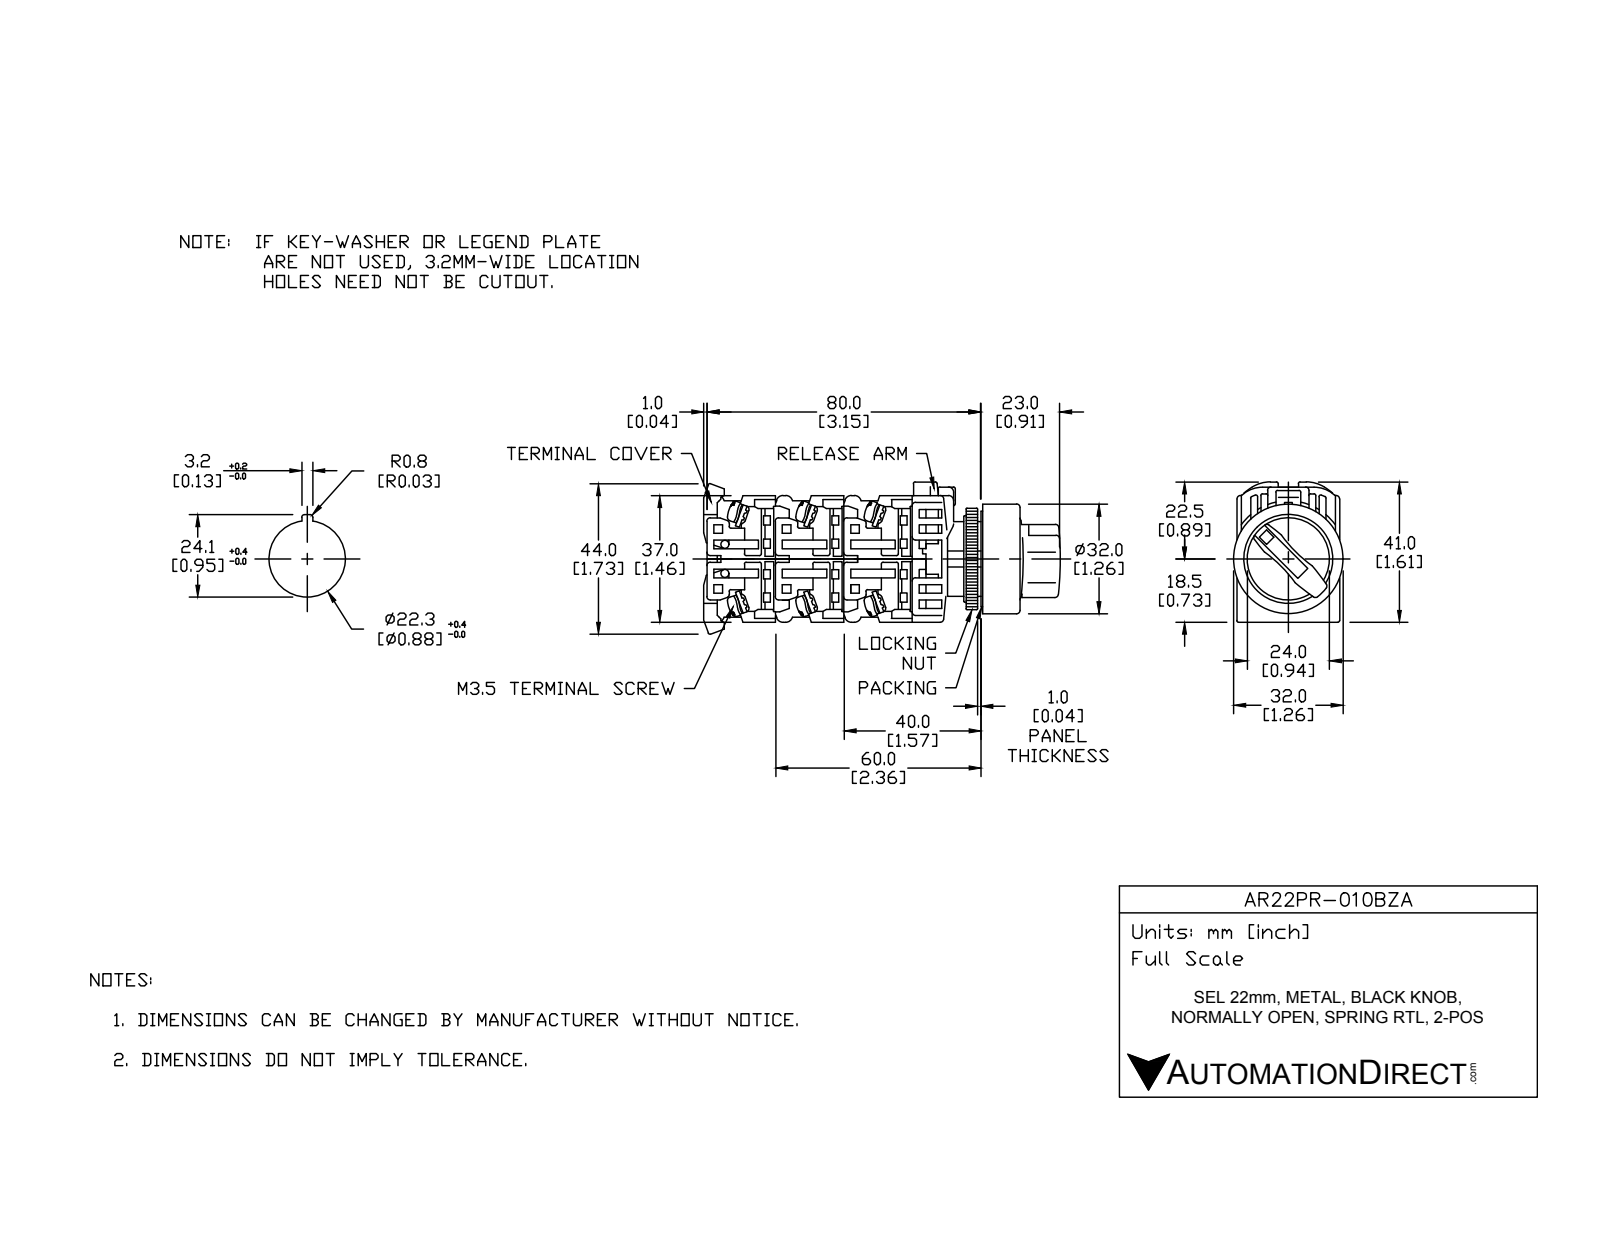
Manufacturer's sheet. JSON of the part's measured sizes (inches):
{"part_name": "AR22PR-010BZA", "step_written_by": "SolidWorks 2017 (AUTOMOTIVE_DESIGN)", "units": "inches", "bodies": {"solids": 12, "faces": 322, "planar": 221, "cylindrical": 81, "other": 20}, "overall_size": [2.52, 1.614, 1.26], "volume_in3": 1.794, "surface_area_in2": 31.2, "round_holes": [[0.858, 1], [0.866, 1], [0.984, 1], [1.22, 1]], "round_bosses_or_shafts": [[0.197, 2], [1.26, 1], [1.201, 1], [1.173, 1], [0.945, 1], [0.856, 1], [0.669, 1]], "partial_cylinders_radius": [[0.02, 23], [0.039, 6], [0.069, 4], [0.197, 4], [0.157, 2], [0.472, 1], [0.653, 1], [0.693, 1]], "face_to_face_distances": [0.039, 0.118, 1.122, 0.709, 0.079, 1.142, 0.433, 1.181, 0.413, 0.315]}
